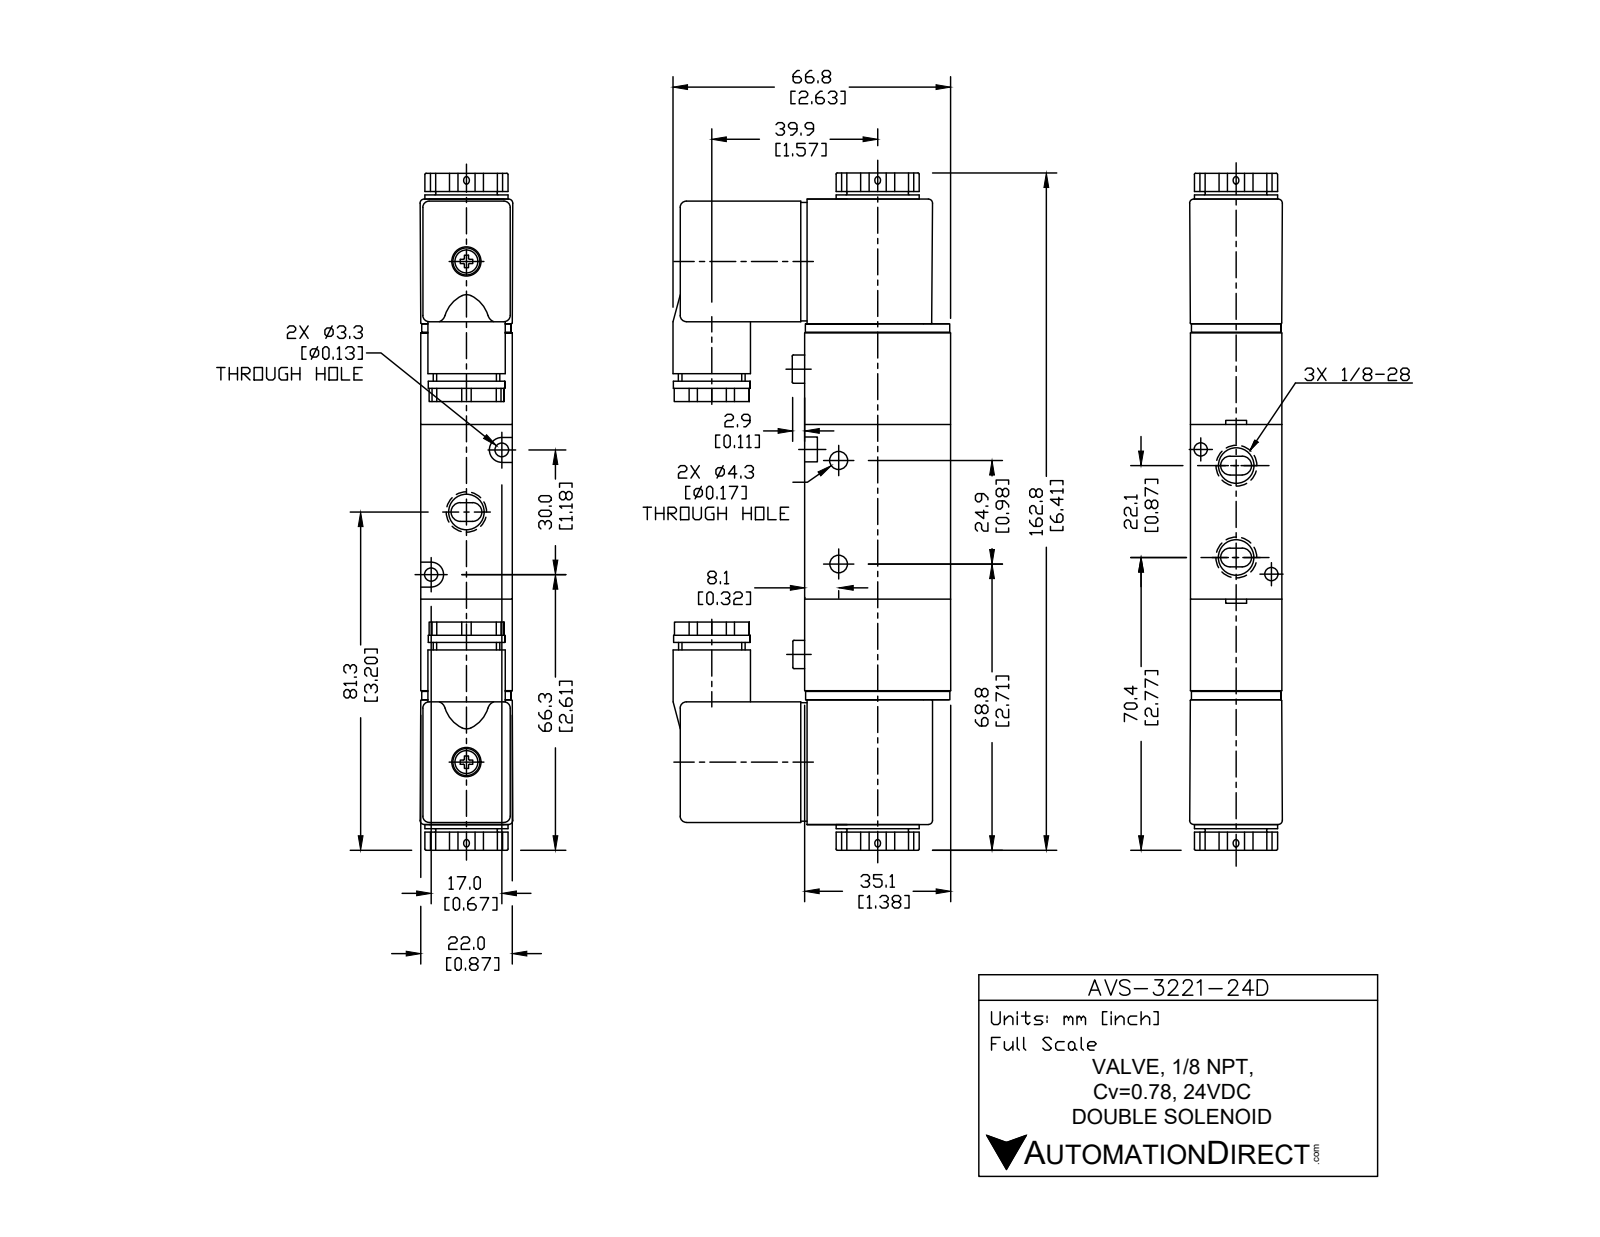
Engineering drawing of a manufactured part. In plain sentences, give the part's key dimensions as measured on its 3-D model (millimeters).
The part is named "AVS-3221-24D". Its 3-D file was written by "SolidWorks 2015 (CONFIG_CONTROL_DESIGN)". It is 5 solids with 252 faces: 138 planar, 82 cylindrical and 32 other. Overall it measures 162.8 by 66.7 by 22 millimeters. Its volume is 153 516 cubic millimeters and its surface area 33 903 square millimeters. Round holes: 3 of diameter 8.43, 2 of diameter 3.3, 2 of diameter 4.3, 1 of diameter 9.3. Round bosses or shafts: 2 of diameter 6.8, 1 of diameter 20, 1 of diameter 18.6, 1 of diameter 18.4, 1 of diameter 16, 1 of diameter 14.8. Partial cylindrical surfaces (rounded edges, fillets, slot ends): 20 of radius 1, 12 of radius 0.5, 2 of radius 3. The main face-to-face distances are 0.5, 22.6, 21.5, 21, 42, 22.82, 22.38, 22, 53.7, 95.7. The hole center spacings are 17.24, 9.35, 9.39, 11, 11.1, 22.1, 25, 27.35.
